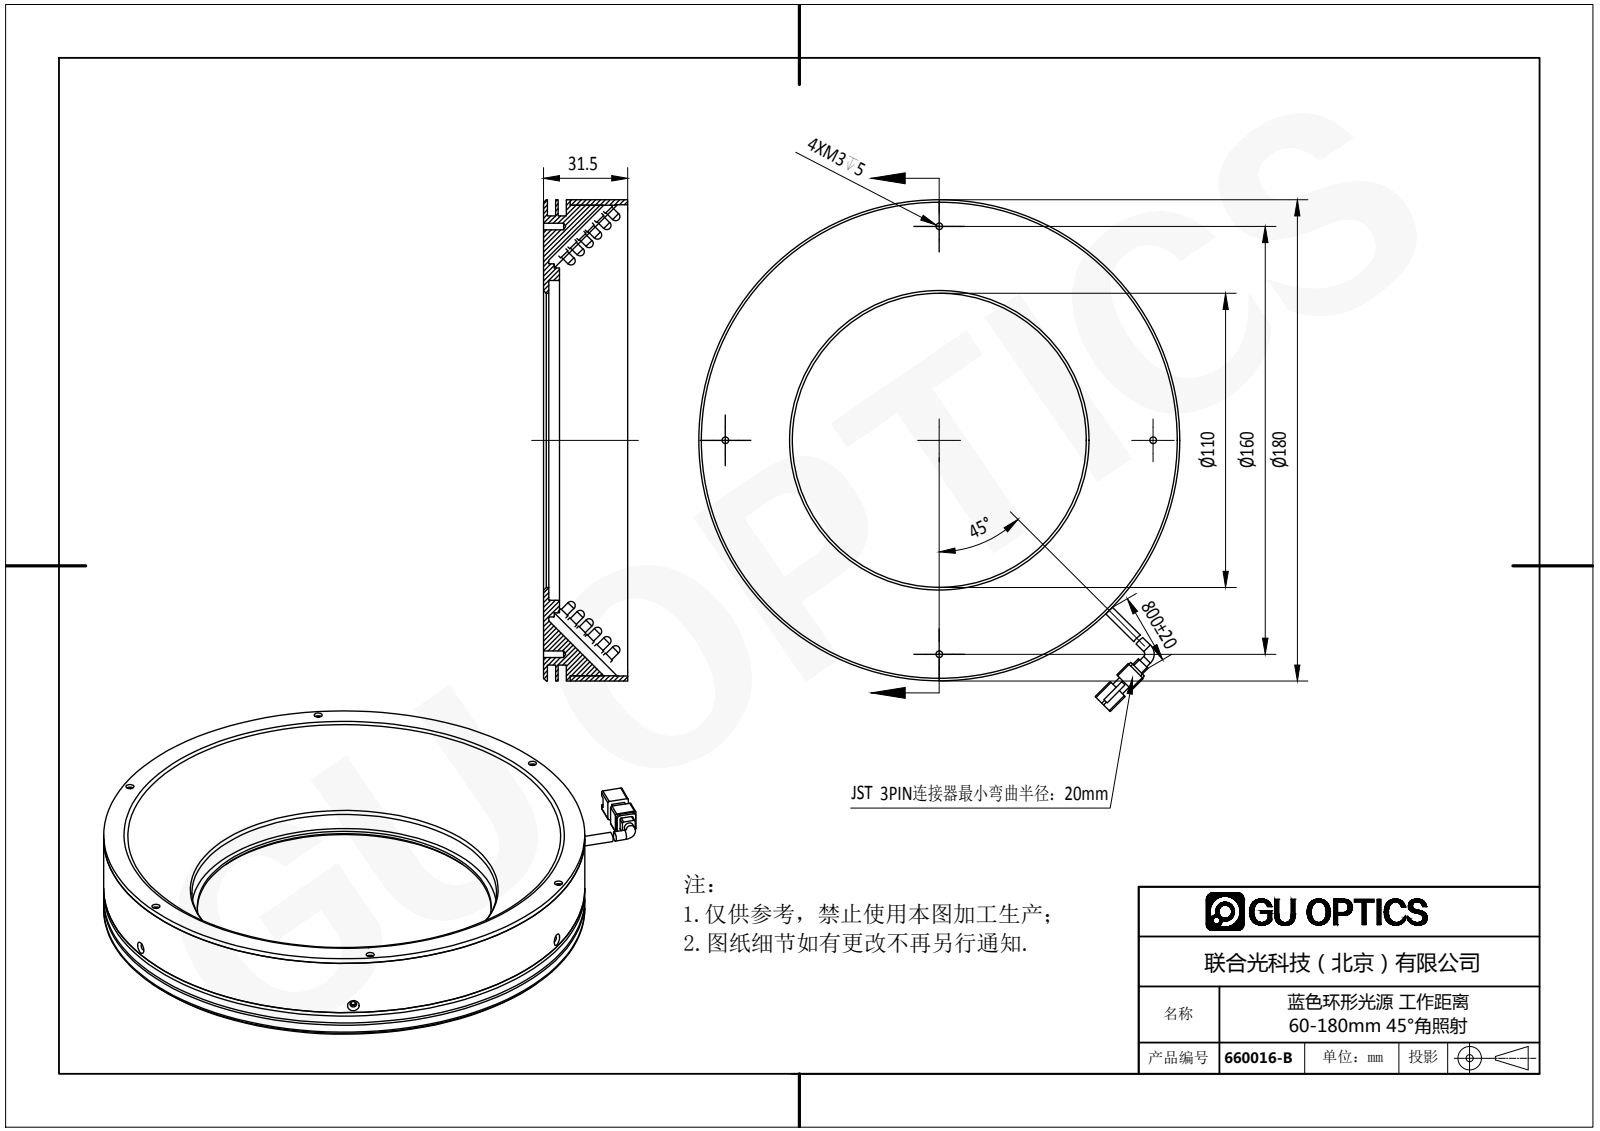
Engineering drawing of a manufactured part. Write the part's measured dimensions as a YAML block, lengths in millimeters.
part_name: "660016-B"
step_written_by: "SolidWorks 2016 (AUTOMOTIVE_DESIGN)"
units: millimeters
bodies: {solids: 546, faces: 9482, planar: 6561, cylindrical: 2312, other: 609}
overall_size: [191.47, 180, 33.5]
volume: 236719
surface_area: 217058
round_holes:
  - {diameter: 3.5, count: 7}
  - {diameter: 1.25, count: 6}
  - {diameter: 1.5, count: 6}
  - {diameter: 3, count: 6}
  - {diameter: 1.6, count: 4}
  - {diameter: 2.5, count: 4}
  - {diameter: 2.4, count: 3}
  - {diameter: 110, count: 1}
  - {diameter: 114, count: 1}
  - {diameter: 119.6, count: 1}
  - {diameter: 172.4, count: 1}
round_bosses_or_shafts:
  - {diameter: 3.8, count: 540}
  - {diameter: 3, count: 540}
  - {diameter: 3.5, count: 2}
  - {diameter: 180, count: 1}
  - {diameter: 176, count: 1}
  - {diameter: 168, count: 1}
  - {diameter: 132, count: 1}
  - {diameter: 129, count: 1}
partial_cylinders:
  - {radius: 0.5, count: 8}
  - {radius: 1, count: 4}
  - {radius: 7.5, count: 1}
face_to_face_distances: [4, 31.5, 2, 0.5, 1.5, 4.5, 3, 2.5, 5.5, 8.5]
hole_center_spacings: [87.5, 151.56, 39.06, 51.47, 128.2, 151.55, 167.26, 170.58]
